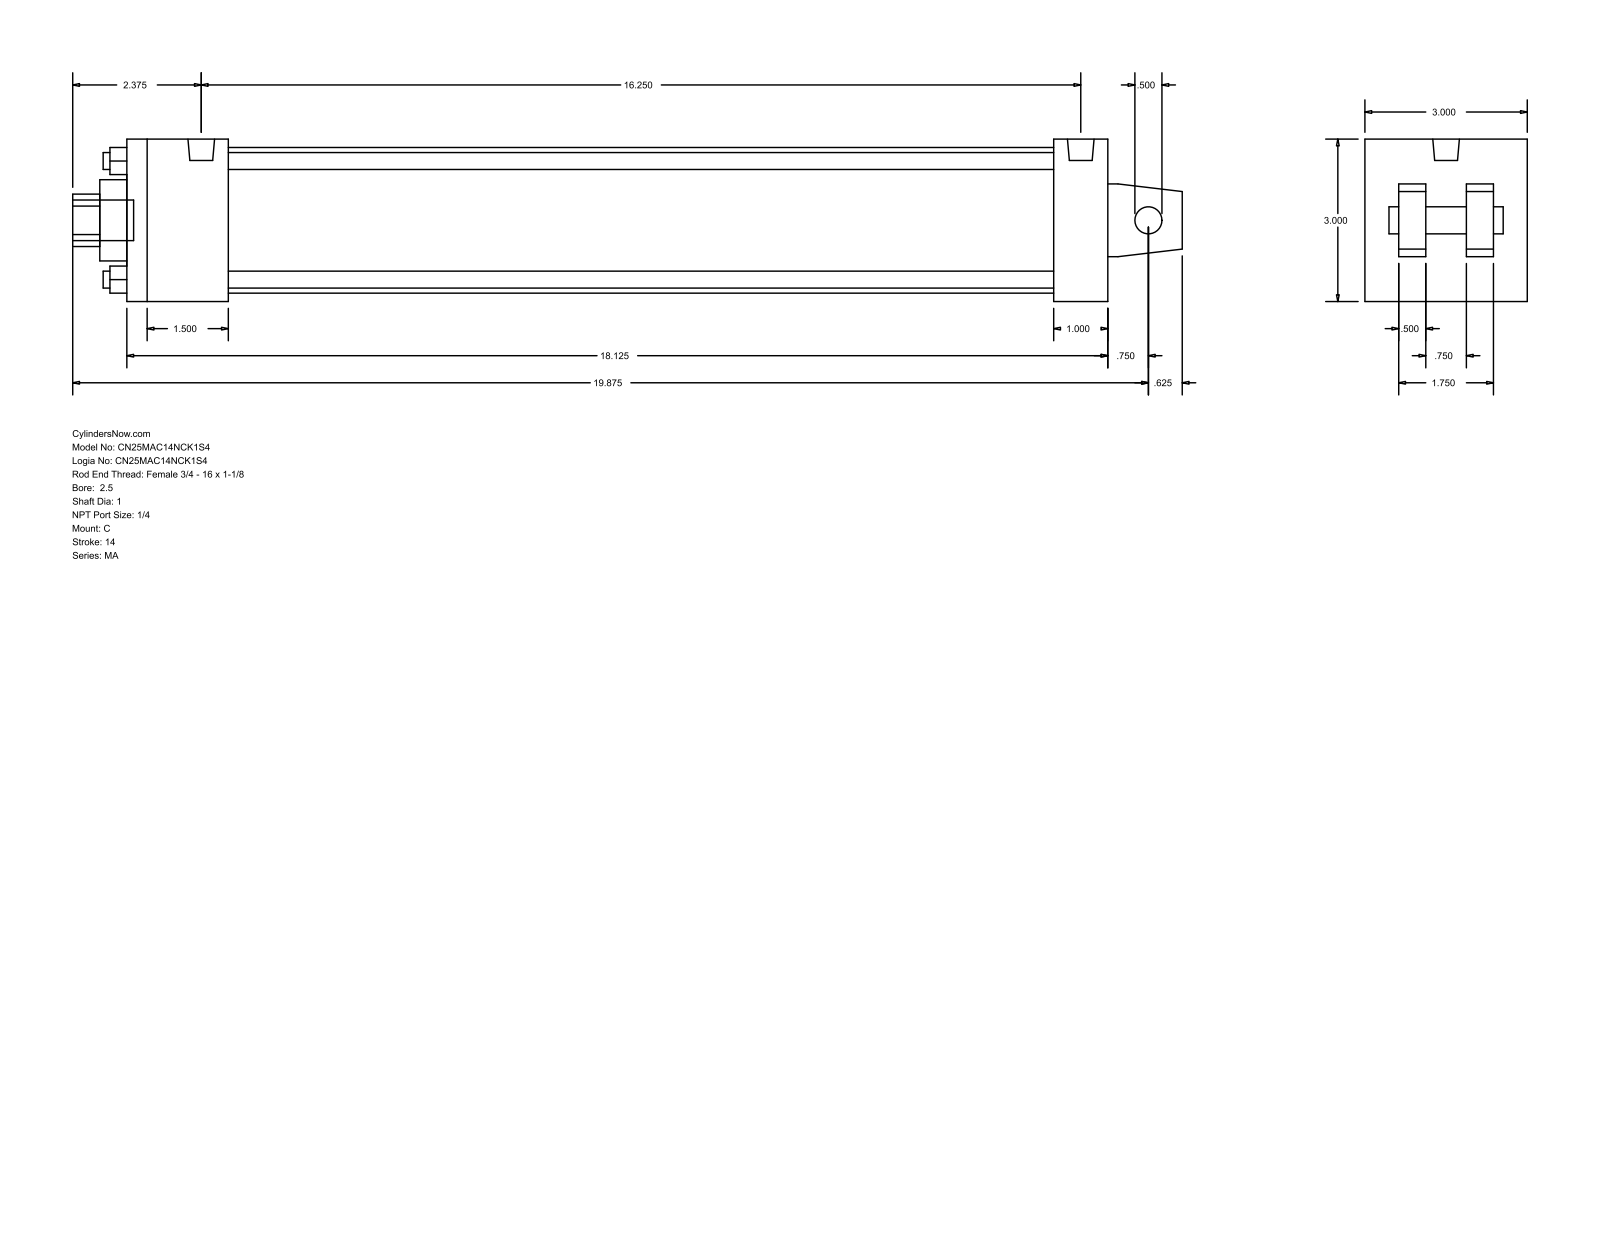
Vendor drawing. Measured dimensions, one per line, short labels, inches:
name: MA_C__0250_1
written by: GSSL Pune (CONFIG_CONTROL_DESIGN)
unit: in
bodies: 0 solids, 103 faces (76 planar, 27 cylindrical, 0 other)
size: 20.5 × 3 × 3
holes: 4× ⌀0.313, 1× ⌀0.5, 1× ⌀1, 1× ⌀1.5, 1× ⌀2.69
bosses: 4× ⌀0.313, 2× ⌀0.492, 1× ⌀0.75
rounds: 1× R0.484
face distances: 3, 1.875, 18.125, 0.5, 0.625, 2.375, 1.125, 17.125, 15.25, 16.25
hole spacings: 1.548, 2.19, 3.097
